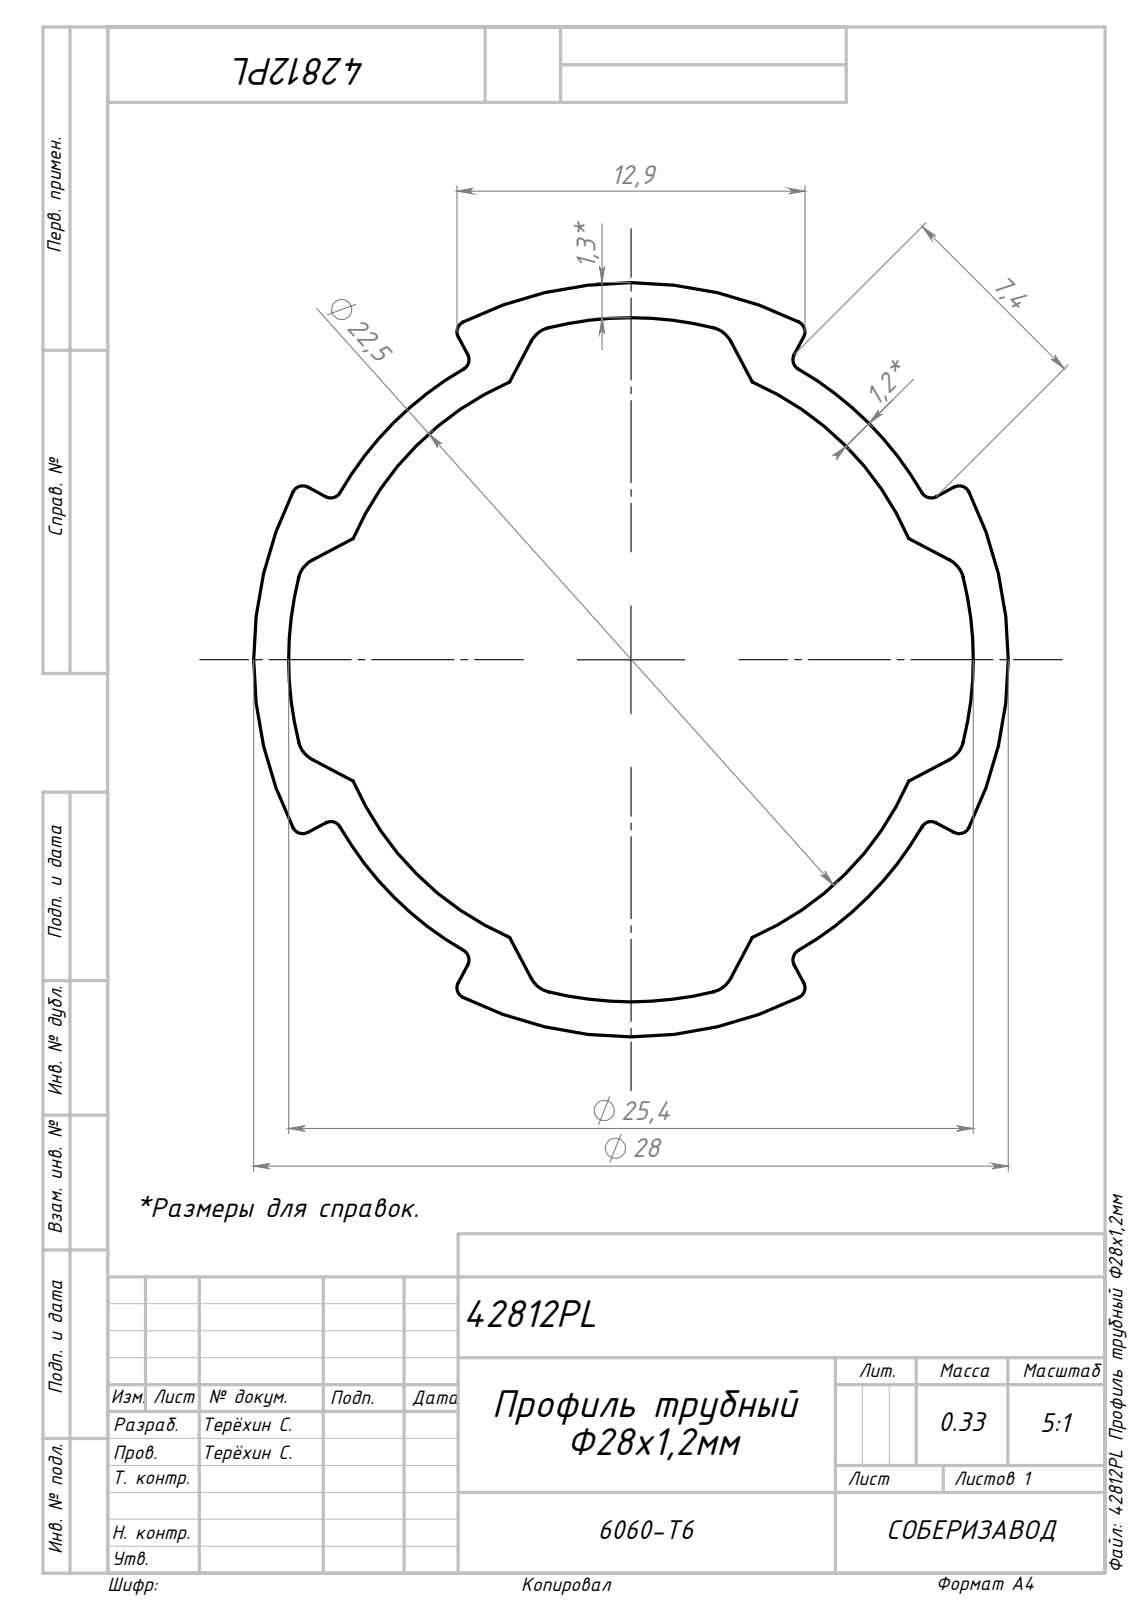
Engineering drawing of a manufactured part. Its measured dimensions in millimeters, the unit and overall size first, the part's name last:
Units: millimetres
Overall size (bounding box): 1000 × 28 × 28
Partial cylindrical surfaces — rounded edges, fillets, slot ends (radius × count): R0.4 ×16, R1 ×8, R11.25 ×1, R12.45 ×1, R12.7 ×1, R14 ×1
Main face-to-face distances: 17.58, 1000
Volume: 122 833 mm³ · Surface area: 172 988 mm²
Bodies: 1 solid, 64 faces (18 planar, 46 cylindrical, 0 other)
Part name (STEP PRODUCT): 42812PL Профиль трубный Φ28х1,2мм_00; Сборка7
STEP written by: SolidWorks 2022 (AUTOMOTIVE_DESIGN)
